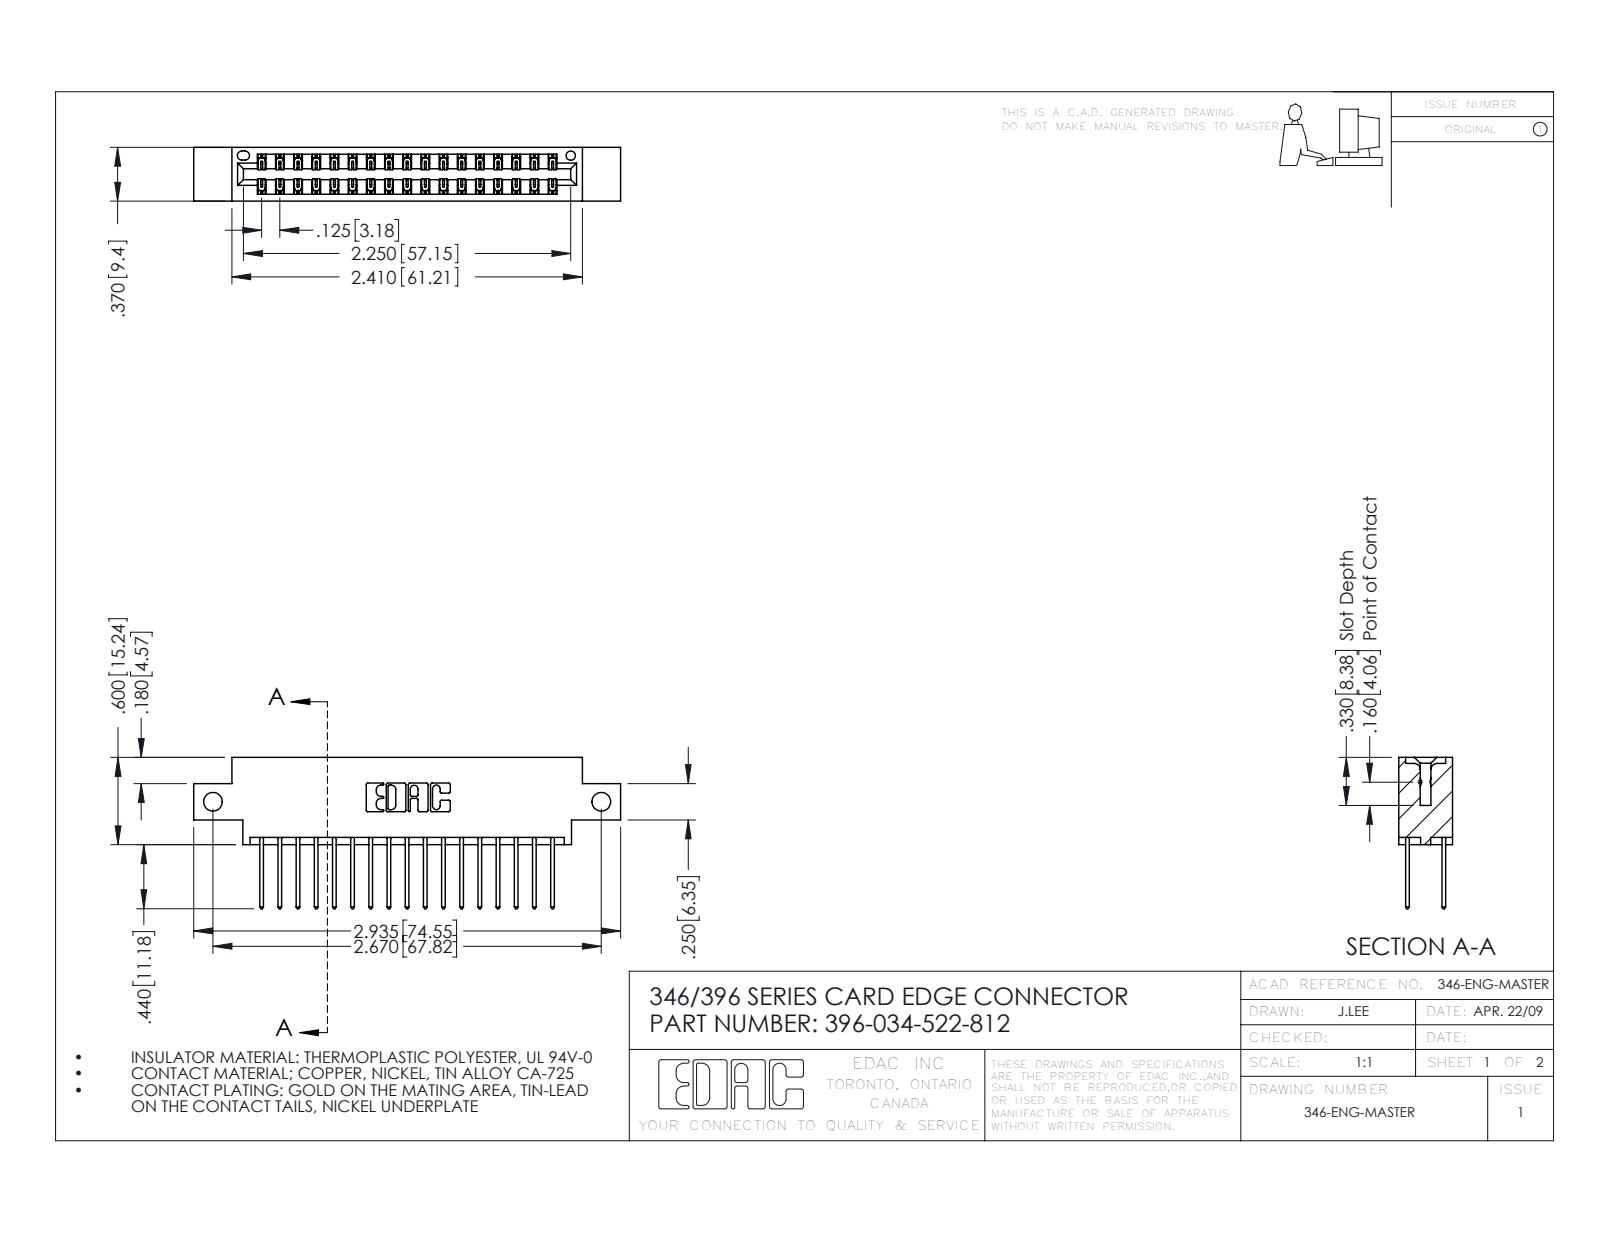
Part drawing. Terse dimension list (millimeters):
name: 346 Part_0.170 Offset - Side Mount; 345-292-001_345-293-122; 396-034-522-812
written by: SolidWorks 2016 (CONFIG_CONTROL_DESIGN)
unit: mm
bodies: 35 solids, 1894 faces (1270 planar, 624 cylindrical, 0 other)
size: 74.5 × 26.4 × 9.4
volume: 6 920 mm³; area: 9 568 mm²
holes: 2× ⌀3.3, 1× ⌀1.6
rounds: 51× R0.2, 34× R0.3, 22× R0.3, 6× R0.2, 6× R0.8, 3× R0.7, 2× R0.4, 2× R0.6
face distances: 1.2, 8.2, 6.4, 9.4, 1.8, 7.6, 0.6, 7, 3.8, 5.6
hole spacings: 67.8
